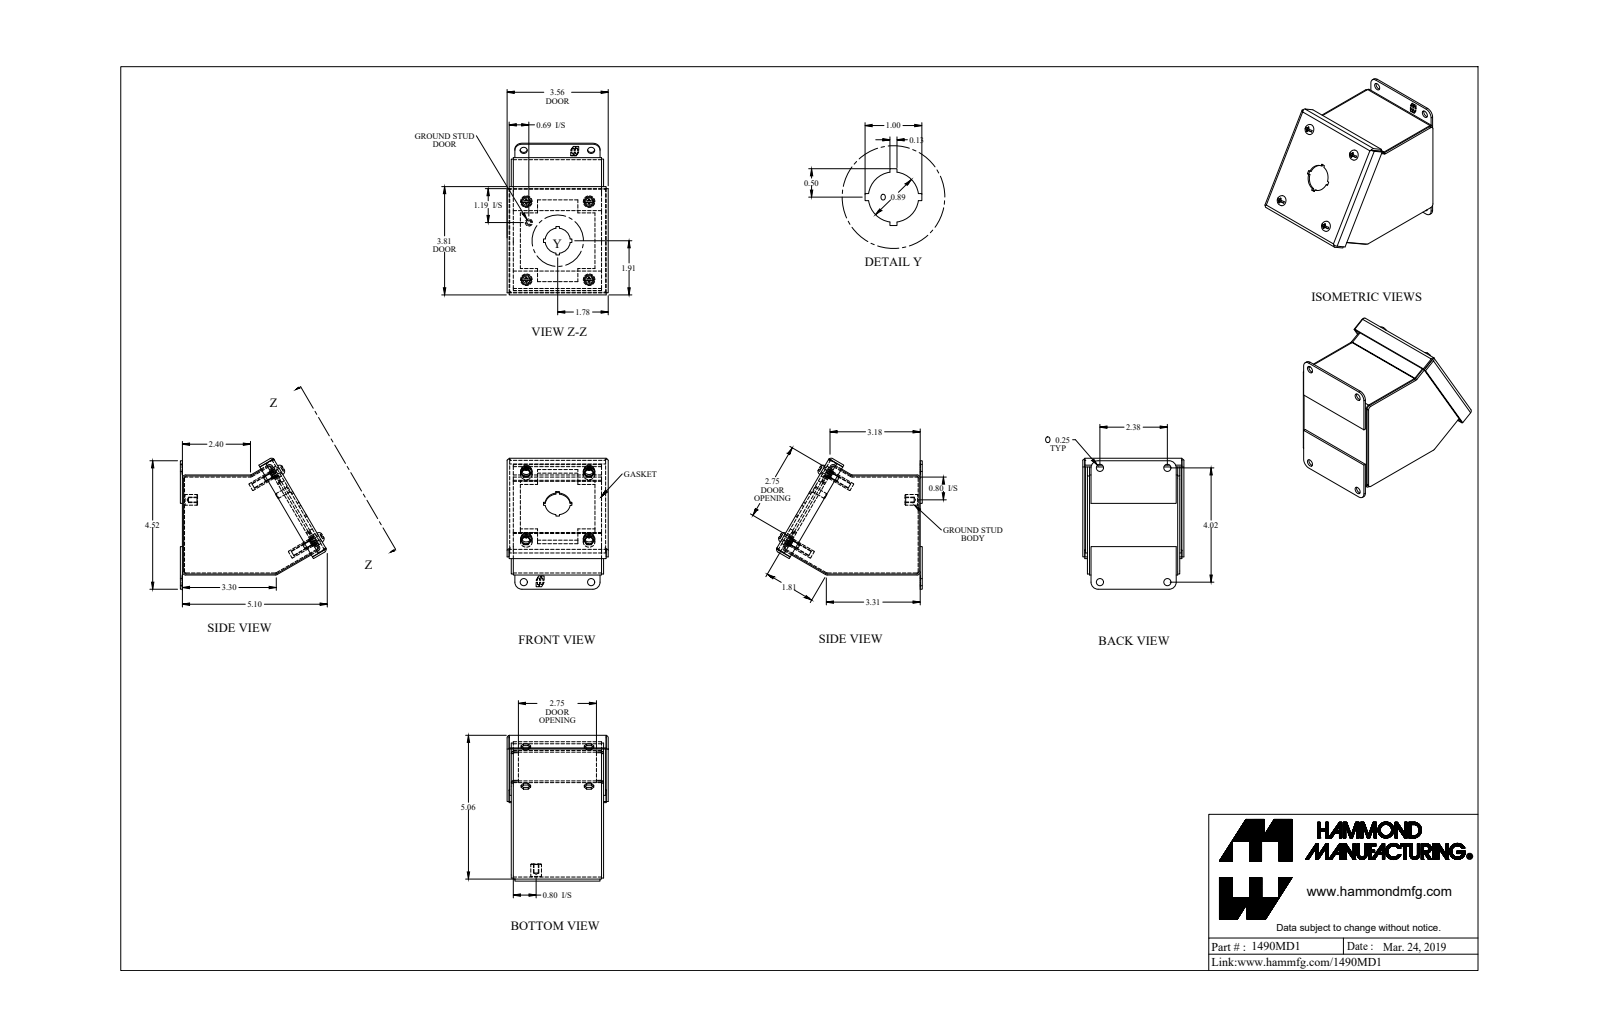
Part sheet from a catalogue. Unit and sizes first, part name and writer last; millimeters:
Units: millimetres
Overall size (bounding box): 131.5 × 117.7 × 90.5
Round holes (diameter × count): ⌀6.4 ×8, ⌀4 ×4, ⌀4 ×1, ⌀22.2 ×1
Round bosses / shafts (diameter × count): ⌀9.9 ×4, ⌀7 ×4, ⌀4.8 ×4, ⌀3.8 ×4, ⌀9.5 ×1
Partial cylindrical surfaces — rounded edges, fillets, slot ends (radius × count): R2.7 ×18, R0.9 ×12, R3.2 ×4, R4.1 ×4, R4.3 ×4, R6.4 ×4
Main face-to-face distances: 1.8, 1.8, 78.9, 87.6, 80.7, 82.6, 80.7, 3.7, 89.5, 85.8
Hole centre spacings: 56.1, 56.5, 0.4, 44.8, 44.8, 60.3, 69.8, 69.9
Volume: 118 800 mm³ · Surface area: 136 800 mm²
Bodies: 19 solids, 532 faces (354 planar, 140 cylindrical, 38 other)
Part name (STEP PRODUCT): 1490MD1_Default
STEP written by: SolidWorks 2019 (CONFIG_CONTROL_DESIGN)
